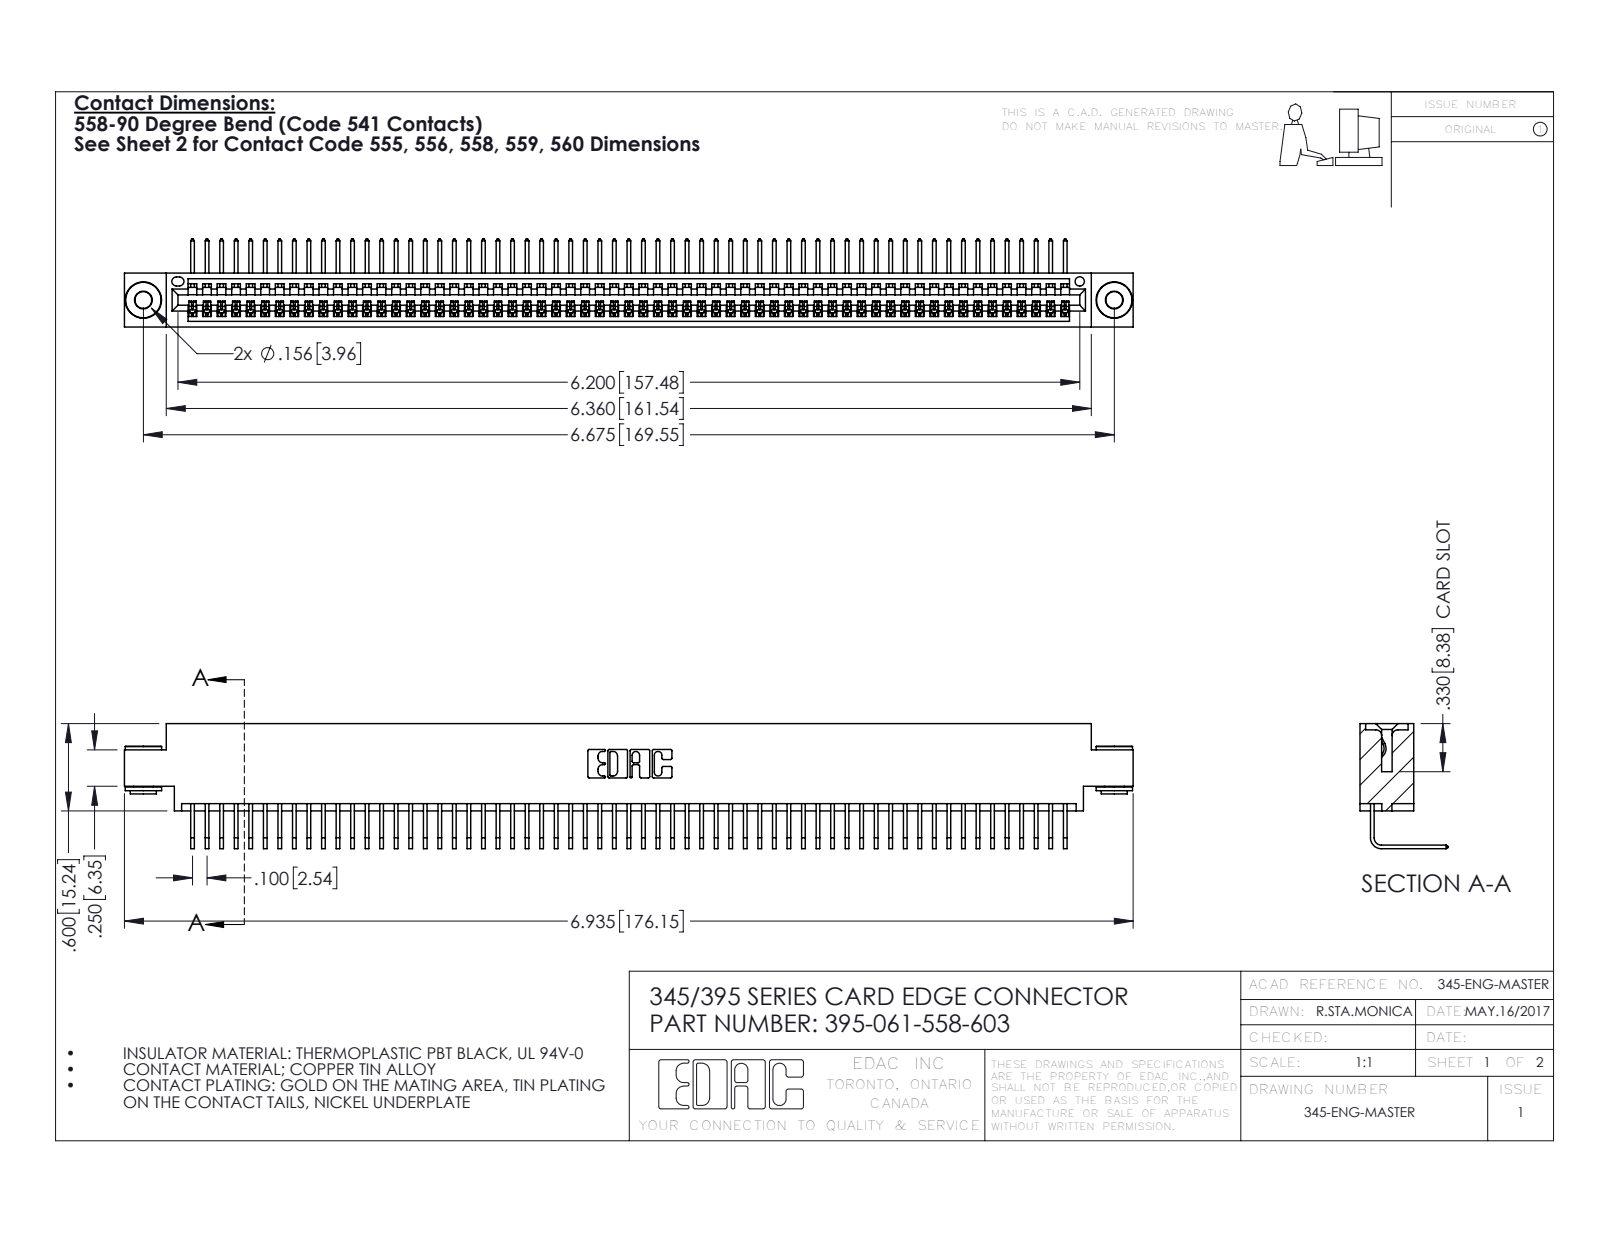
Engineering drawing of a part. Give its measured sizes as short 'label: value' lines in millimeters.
name: 395-061-558-603; 345 Part_0.170 Offset - 0.156 Dia-TH; 345-292-001_558 Tail - 2; 345-250-002_345-250-002-102
written by: SolidWorks 2016 (CONFIG_CONTROL_DESIGN)
unit: mm
bodies: 64 solids, 3828 faces (2656 planar, 1164 cylindrical, 8 other)
size: 176.1 × 21.8 × 15.4
volume: 16 990 mm³; area: 24 380 mm²
holes: 2× ⌀2.9, 2× ⌀4, 1× ⌀1.6
bosses: 2× ⌀6.4, 2× ⌀4.6, 2× ⌀3.5
rounds: 122× R0.2, 22× R0.3, 6× R0.2, 6× R0.8, 3× R0.7, 2× R0.8, 2× R1, 1× R0.4
face distances: 1.8, 7.6, 9.4, 5.1, 2.5, 6.9, 0.6, 5.7, 4.4, 3.8
hole spacings: 6.9, 163.6, 169.5
